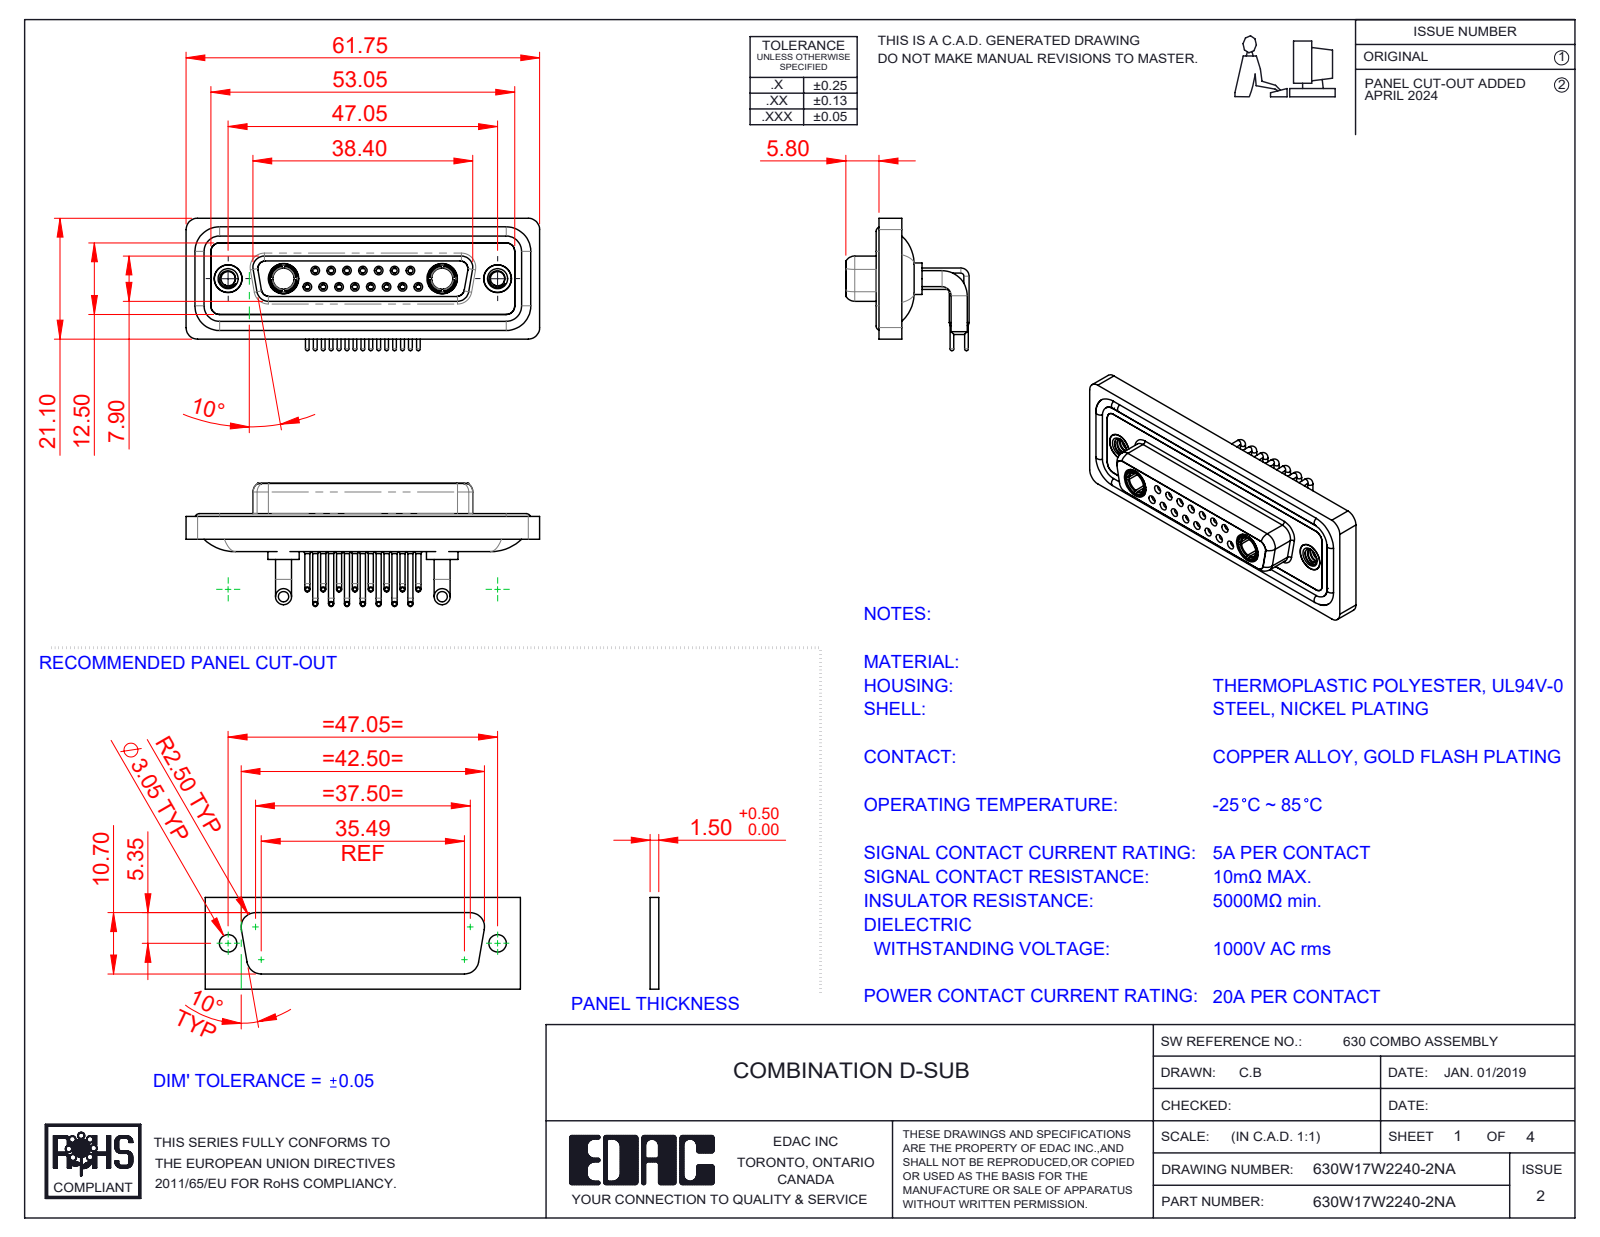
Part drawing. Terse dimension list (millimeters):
name: 630Combo Shell Rear_25 Contacts; 630Combo Shell Front_25 Contacts; 630Combo Threaded Rivet_A; 630Combo Housing_17W2 (+5 more)
written by: SolidWorks 2023 (CONFIG_CONTROL_DESIGN)
unit: mm
bodies: 26 solids, 1331 faces (388 planar, 581 cylindrical, 362 other)
size: 61.75 × 23.12 × 21.53
volume: 8 479 mm³; area: 14 533 mm²
holes: 15× ⌀0.9, 15× ⌀1.1, 15× ⌀1.5, 15× ⌀2, 8× ⌀1.6, 7× ⌀1.7, 4× ⌀4.85, 2× ⌀2.5, 2× ⌀3.7, 2× ⌀4, 2× ⌀4.05, 2× ⌀5
bosses: 15× ⌀0.9, 15× ⌀0.65, 11× ⌀1.6, 4× ⌀2.8, 2× ⌀5.5, 2× ⌀5.2, 2× ⌀4.96, 2× ⌀4.95
rounds: 18× R1.5, 18× R2, 8× R1.35, 8× R1.6, 4× R0.25, 4× R0.5, 4× R0.6, 4× R0.65
face distances: 0.4, 1.8, 4.1, 1.1, 1.6, 3.1, 1.5, 2.5, 3.7, 1.4
hole spacings: 3.16, 2.77, 5.54, 8.31, 5.04, 7.49, 11.08, 5.03
